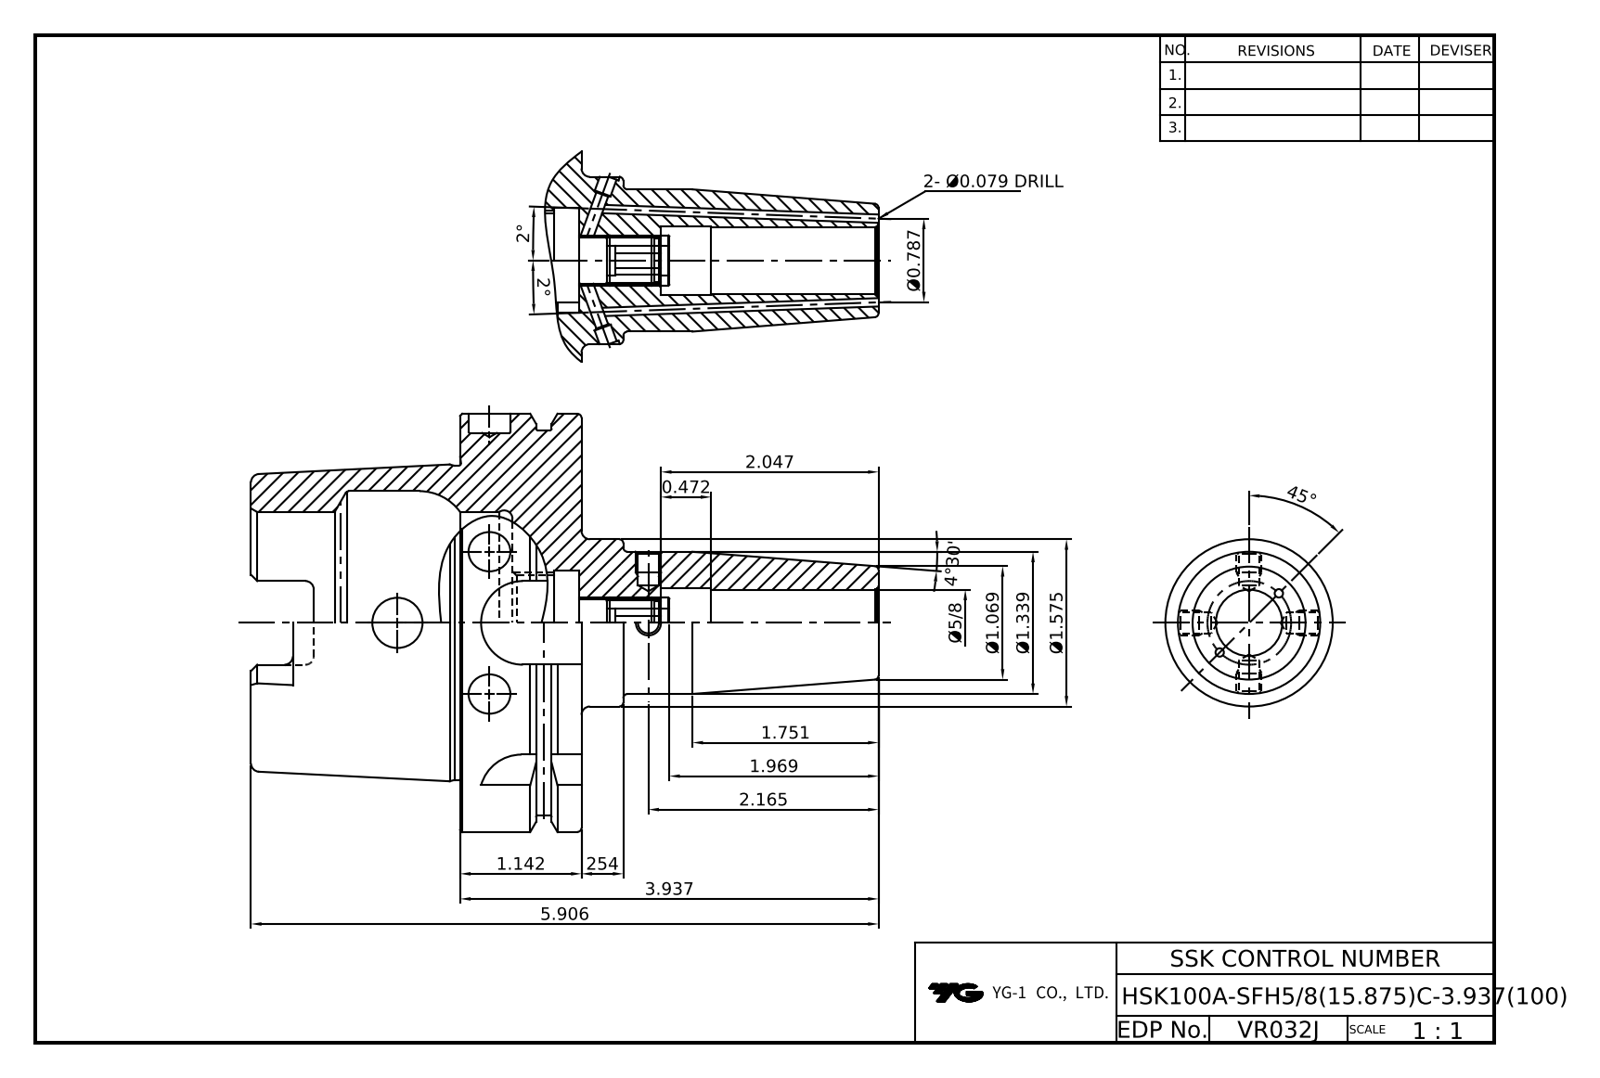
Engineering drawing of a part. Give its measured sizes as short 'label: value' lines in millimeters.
name: LO-HSK100A-SFH15.875C-100
written by: Autodesk Inventor 2022 (AUTOMOTIVE_DESIGN)
unit: mm
bodies: 1 solid, 121 faces (39 planar, 37 cylindrical, 45 other)
size: 150 × 100 × 100
volume: 299 819 mm³; area: 60 350 mm²
holes: 2× ⌀2, 1× ⌀10, 1× ⌀10.92, 1× ⌀12, 1× ⌀15.88, 1× ⌀17.07, 1× ⌀22.38, 1× ⌀25, 1× ⌀53, 1× ⌀63
bosses: 1× ⌀100, 1× ⌀92, 1× ⌀75.41, 1× ⌀40, 1× ⌀34
rounds: 6× R2, 4× R4.88, 4× R10
face distances: 29, 12.5, 16.5, 62.5, 50, 79, 88, 78.5, 28.5, 16
